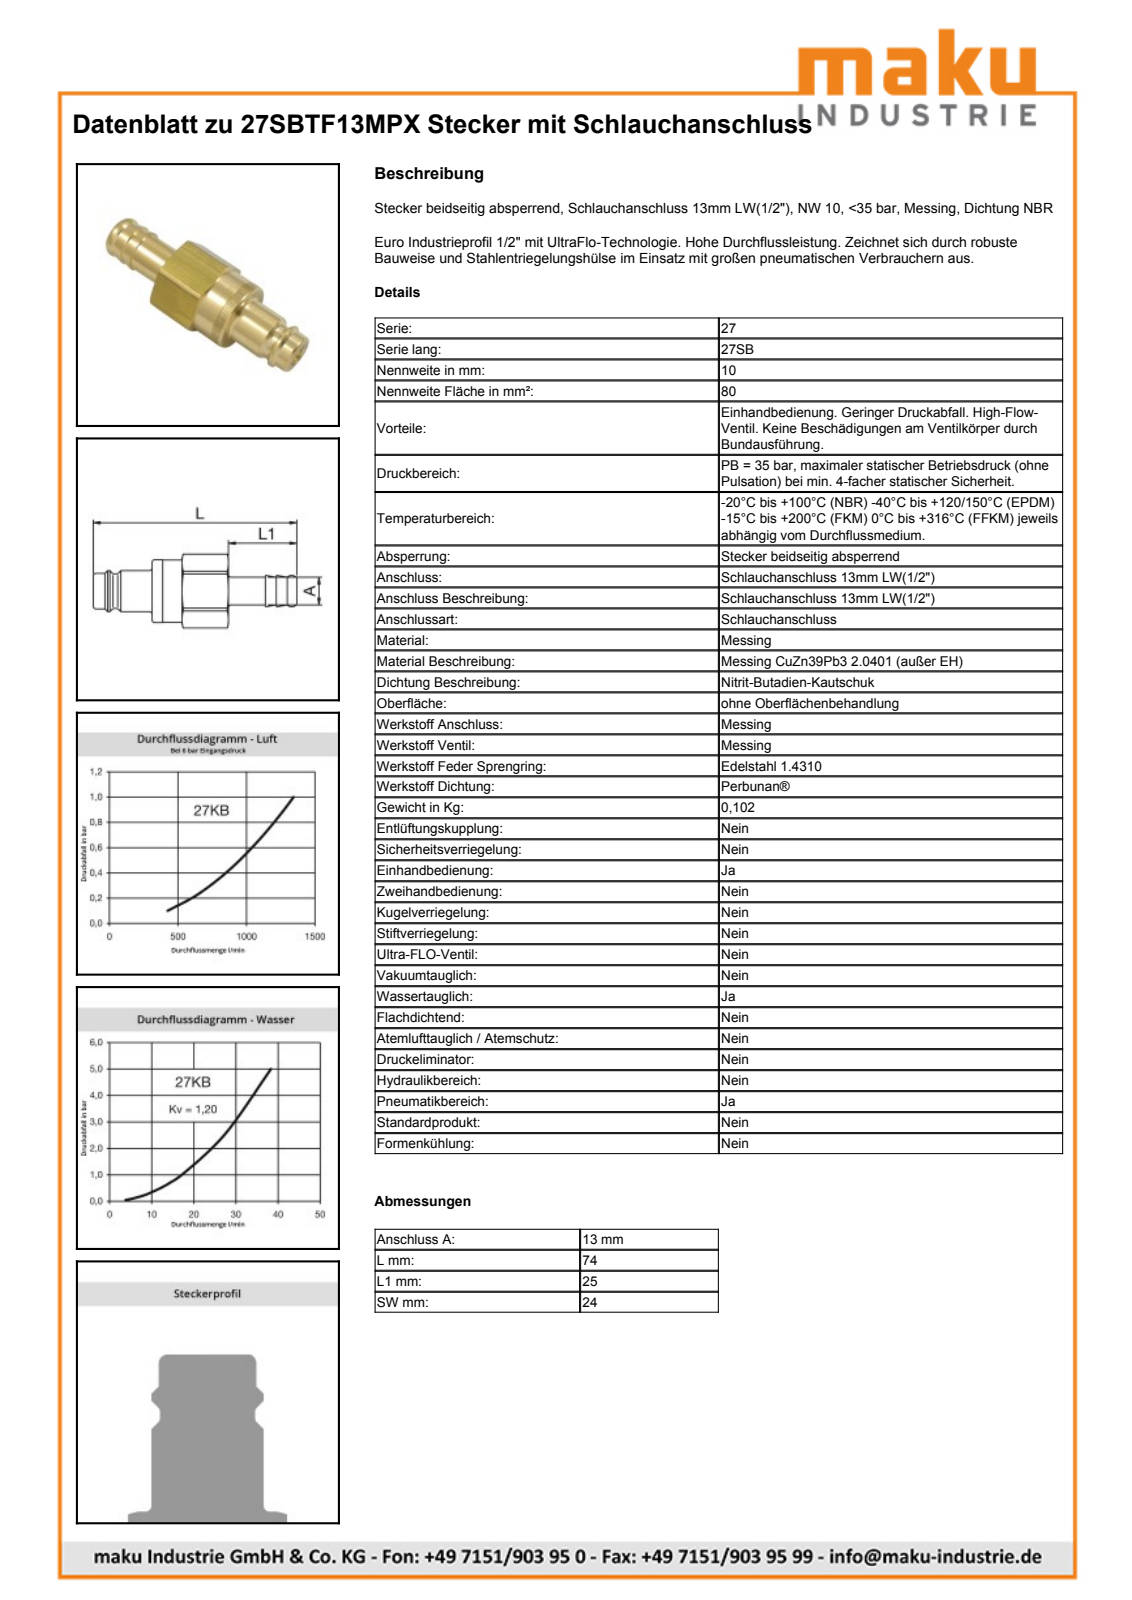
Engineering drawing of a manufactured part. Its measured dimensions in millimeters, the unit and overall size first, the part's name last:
Units: millimetres
Overall size (bounding box): 74.4 × 27.04 × 24.84
Round holes (diameter × count): ⌀19 ×1, ⌀20.3 ×1
Round bosses / shafts (diameter × count): ⌀23 ×1, ⌀22.75 ×1, ⌀18.87 ×1, ⌀18.5 ×1, ⌀15 ×1, ⌀13.1 ×1, ⌀13 ×1, ⌀12.65 ×1
Partial cylindrical surfaces — rounded edges, fillets, slot ends (radius × count): R13.53 ×1
Main face-to-face distances: 24, 25, 27.9, 52.9, 21.5, 49.4, 74.4, 25.4, 3.9, 49
Volume: 19 840 mm³ · Surface area: 5 908 mm²
Bodies: 1 solid, 63 faces (16 planar, 18 cylindrical, 29 other)
Part name (STEP PRODUCT): D106462
STEP written by: Autodesk Inventor 2013 (AUTOMOTIVE_DESIGN)
